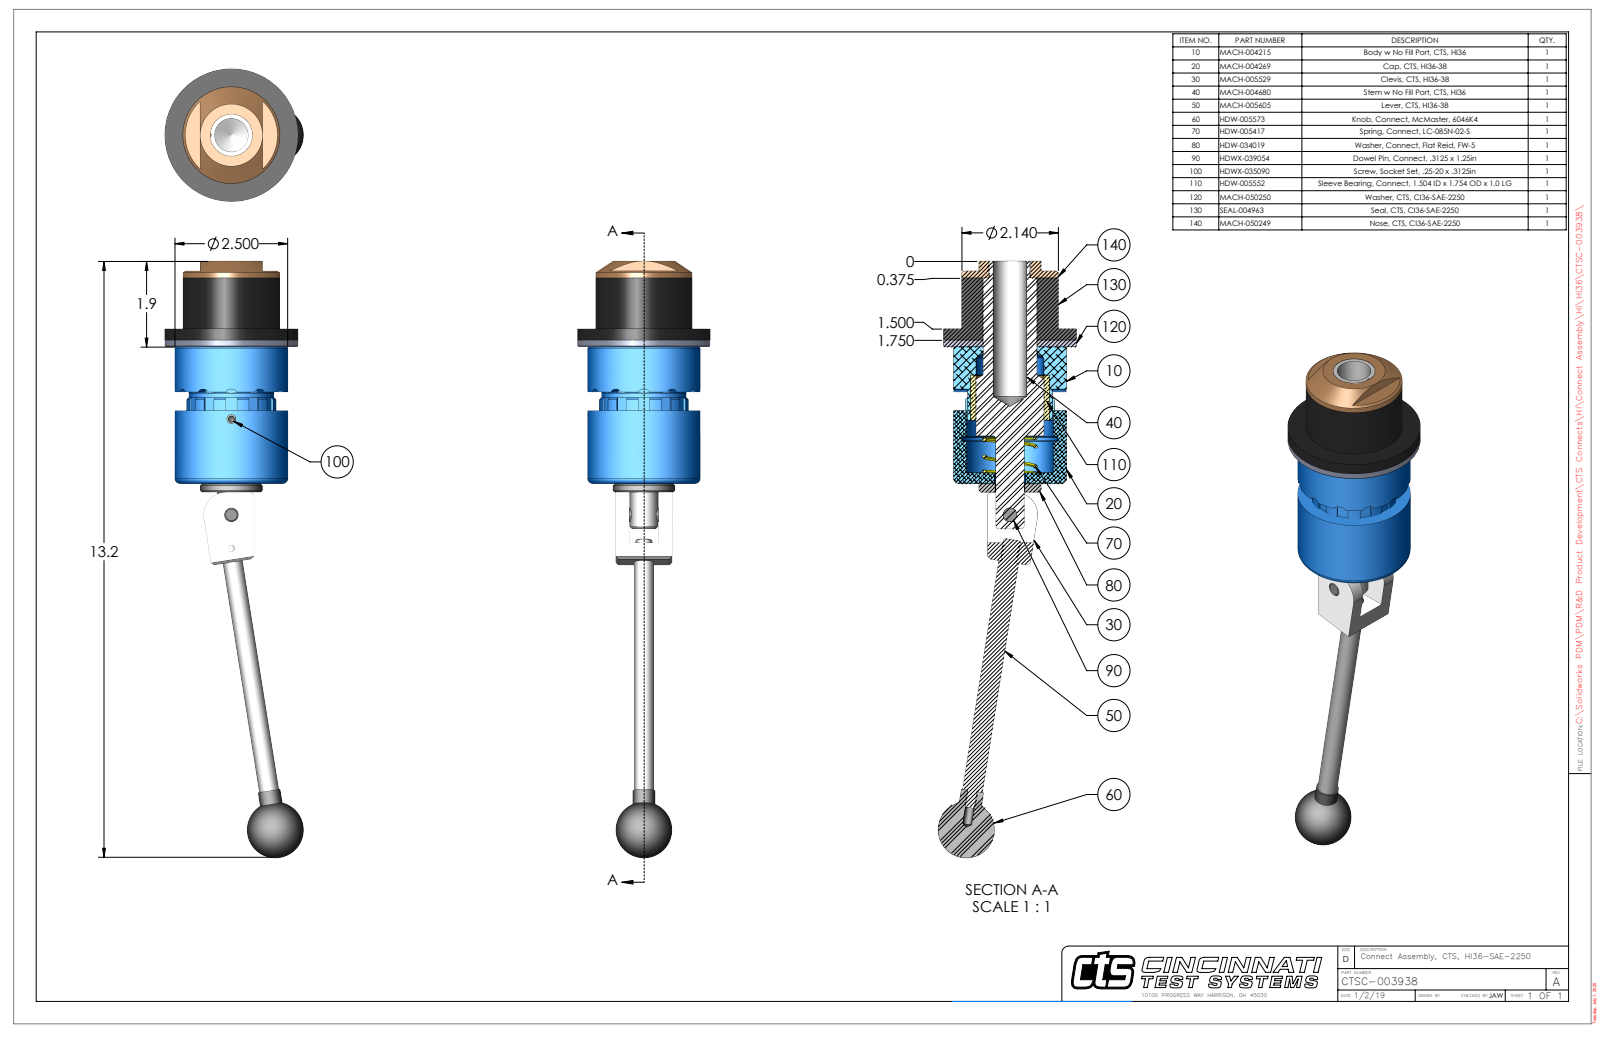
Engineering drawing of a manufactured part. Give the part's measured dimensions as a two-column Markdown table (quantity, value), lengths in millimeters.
| quantity | value |
| --- | --- |
| part name | CTSC-003938 |
| STEP written by | SolidWorks 2023 (AUTOMOTIVE_DESIGN) |
| units | millimeters |
| bodies | 9 solids, 355 faces (153 planar, 126 cylindrical, 76 other) |
| overall size | 335.7 × 77.8 × 74.8 |
| volume | 366 100 mm³ |
| surface area | 84 320 mm² |
| round holes (diameter × count) | 5.1 × 2, 3.8 × 1, 7.9 × 1, 8 × 1, 8 × 1, 16.7 × 1, 17.7 × 1, 19.1 × 1, 30.2 × 1, 30.4 × 1, 54.4 × 1 |
| round bosses / shafts (diameter × count) | 74.8 × 1, 63.5 × 1, 47.6 × 1, 35.1 × 1, 30.1 × 1, 25.4 × 1, 23.4 × 1, 23 × 1 |
| partial cylindrical surfaces (radius × count) | 3 × 12, 0.7 × 2, 12.7 × 1, 24.4 × 1, 25.3 × 1, 29.9 × 1 |
| main face-to-face distances | 3.8, 34.9, 38.7, 77, 80.8, 115.7, 6.4, 28.6, 87.1, 10.2 |
| hole center spacings | 18.8, 53.8, 72.6 |
